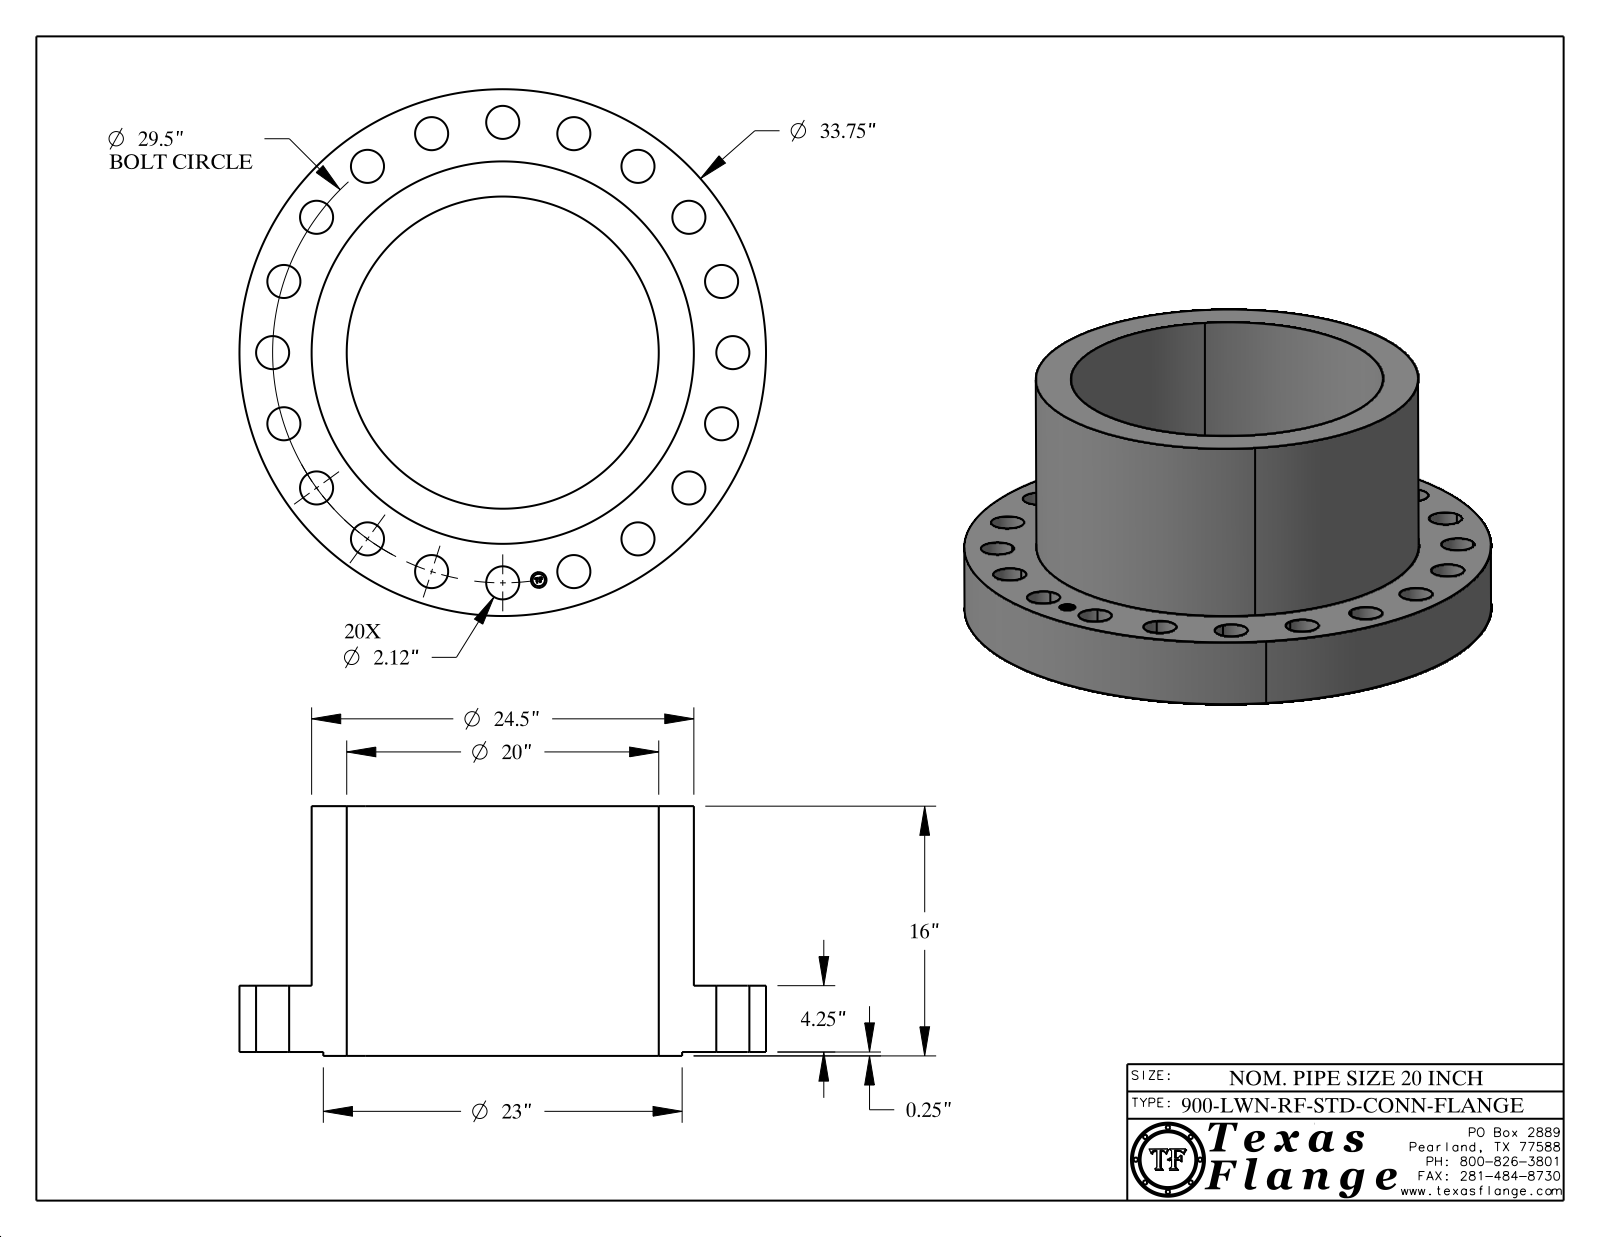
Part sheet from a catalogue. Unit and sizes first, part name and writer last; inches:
Units: inches
Overall size (bounding box): 33.75 × 33.75 × 16
Round holes (diameter × count): ⌀2.12 ×20, ⌀1 ×1, ⌀20 ×1
Round bosses / shafts (diameter × count): ⌀0.061 ×8, ⌀33.75 ×1, ⌀24.5 ×1, ⌀23 ×1, ⌀0.788 ×1
Main face-to-face distances: 4.25, 15.75, 11.5, 0.25, 4.5, 16, 4.495, 4.245, 11.505, 0.298
Hole centre spacings: 14.75, 29.137, 4.615, 17.34, 20.859, 23.866, 26.285, 9.116
Volume: 4 001 in³ · Surface area: 3 945 in²
Bodies: 1 solid, 437 faces (369 planar, 68 cylindrical, 0 other)
Part name (STEP PRODUCT): 20-900-LWN-RF-STD-CONN-FLANGE
STEP written by: CATIA V5 STEP AP214 (AUTOMOTIVE_DESIGN)
